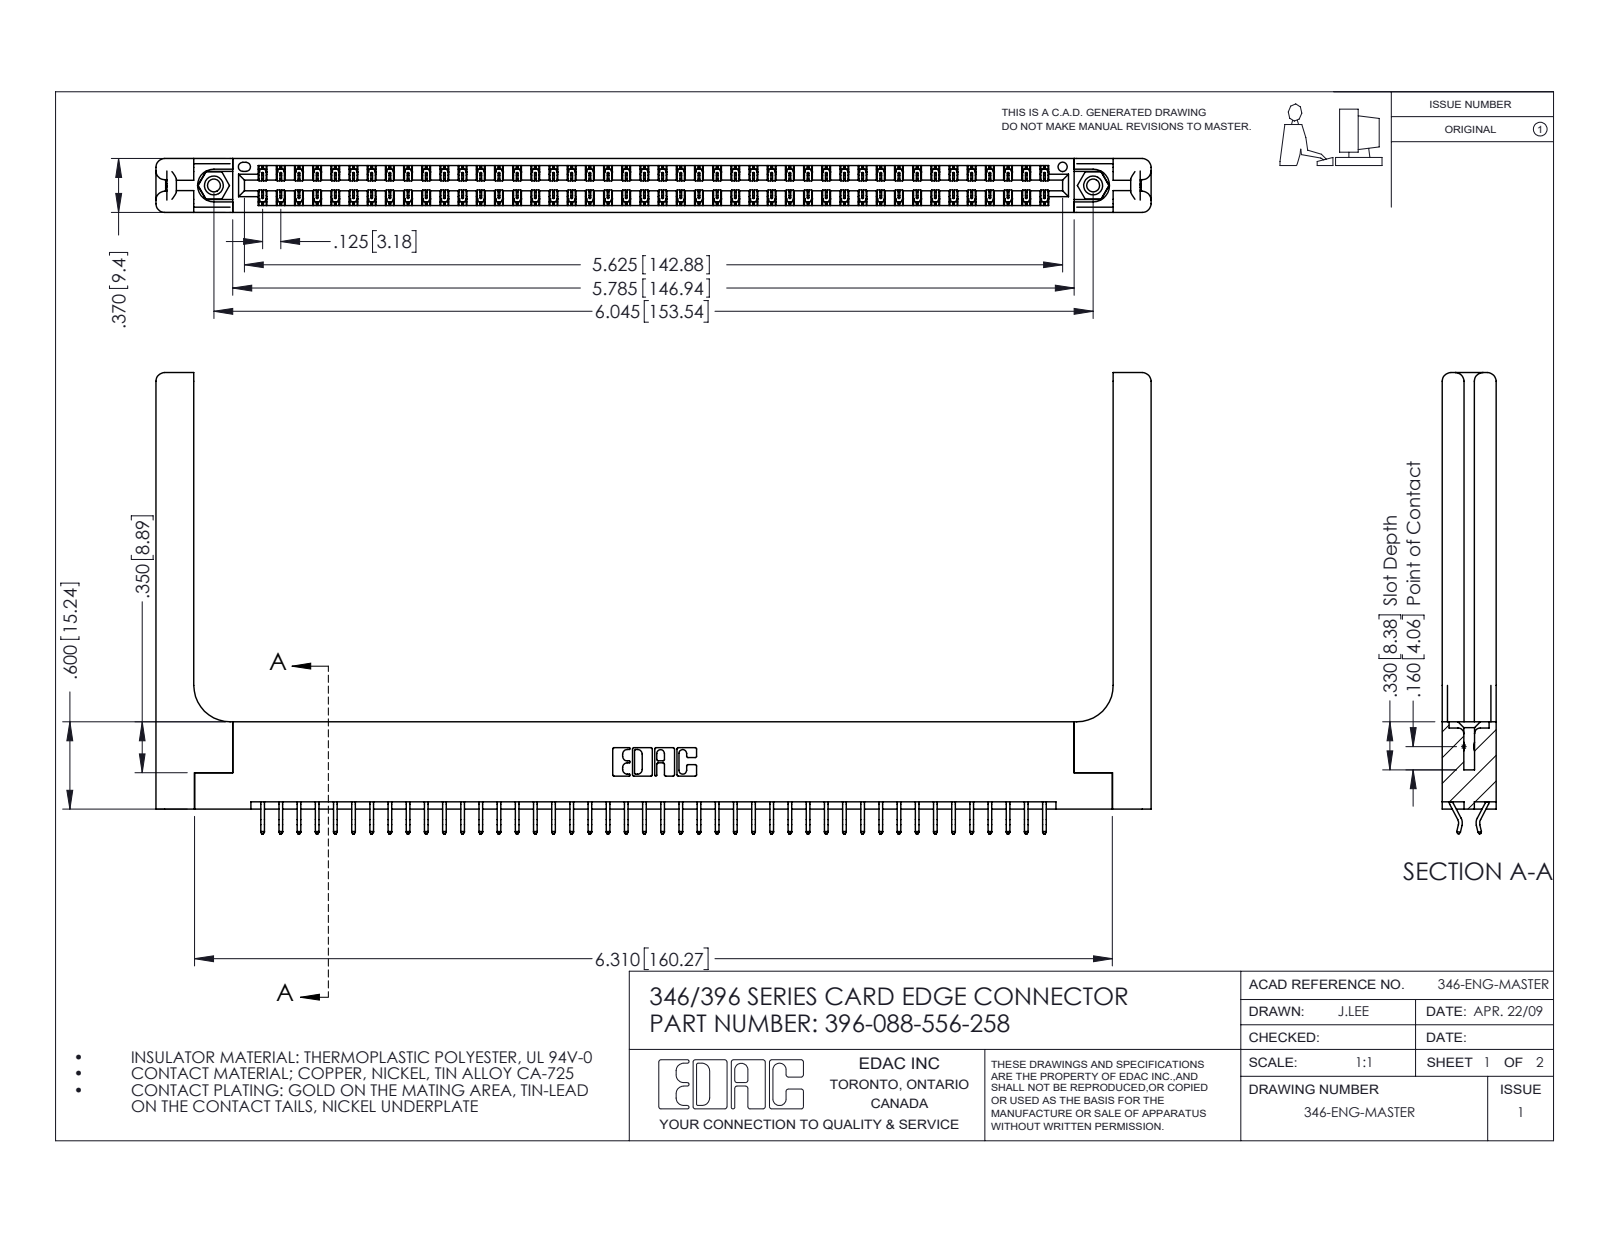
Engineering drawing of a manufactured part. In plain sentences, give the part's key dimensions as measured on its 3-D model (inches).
The part is named "345-292-001_556 Tail; 346-220-058_345-220-058; 345-250-001_345-250-001-102; 346 Part_Flush Mounting Lugs - 0.156 Dia-TH (+1 more)". Its 3-D file was written by "SolidWorks 2016 (CONFIG_CONTROL_DESIGN)". It is 93 solids with 5482 faces: 3656 planar, 1766 cylindrical and 60 other. Overall it measures 6.841 by 3.17 by 0.37 inches. Its volume is 1.492 cubic inches and its surface area 43.76 square inches. Round holes: 2 of diameter 0.089, 2 of diameter 0.125, 2 of diameter 0.156, 1 of diameter 0.064. Round bosses or shafts: 2 of diameter 0.155. Partial cylindrical surfaces (rounded edges, fillets, slot ends): 132 of radius 0.006, 22 of radius 0.01, 16 of radius 0.06, 6 of radius 0.007, 6 of radius 0.031, 3 of radius 0.026, 2 of radius 0.01, 2 of radius 0.014. The main face-to-face distances are 0.37, 0.048, 0.322, 0.072, 0.148, 0.15, 0.25, 0.025, 0.298, 0.275. The hole center spacings are 0.246, 5.836, 6.045.
